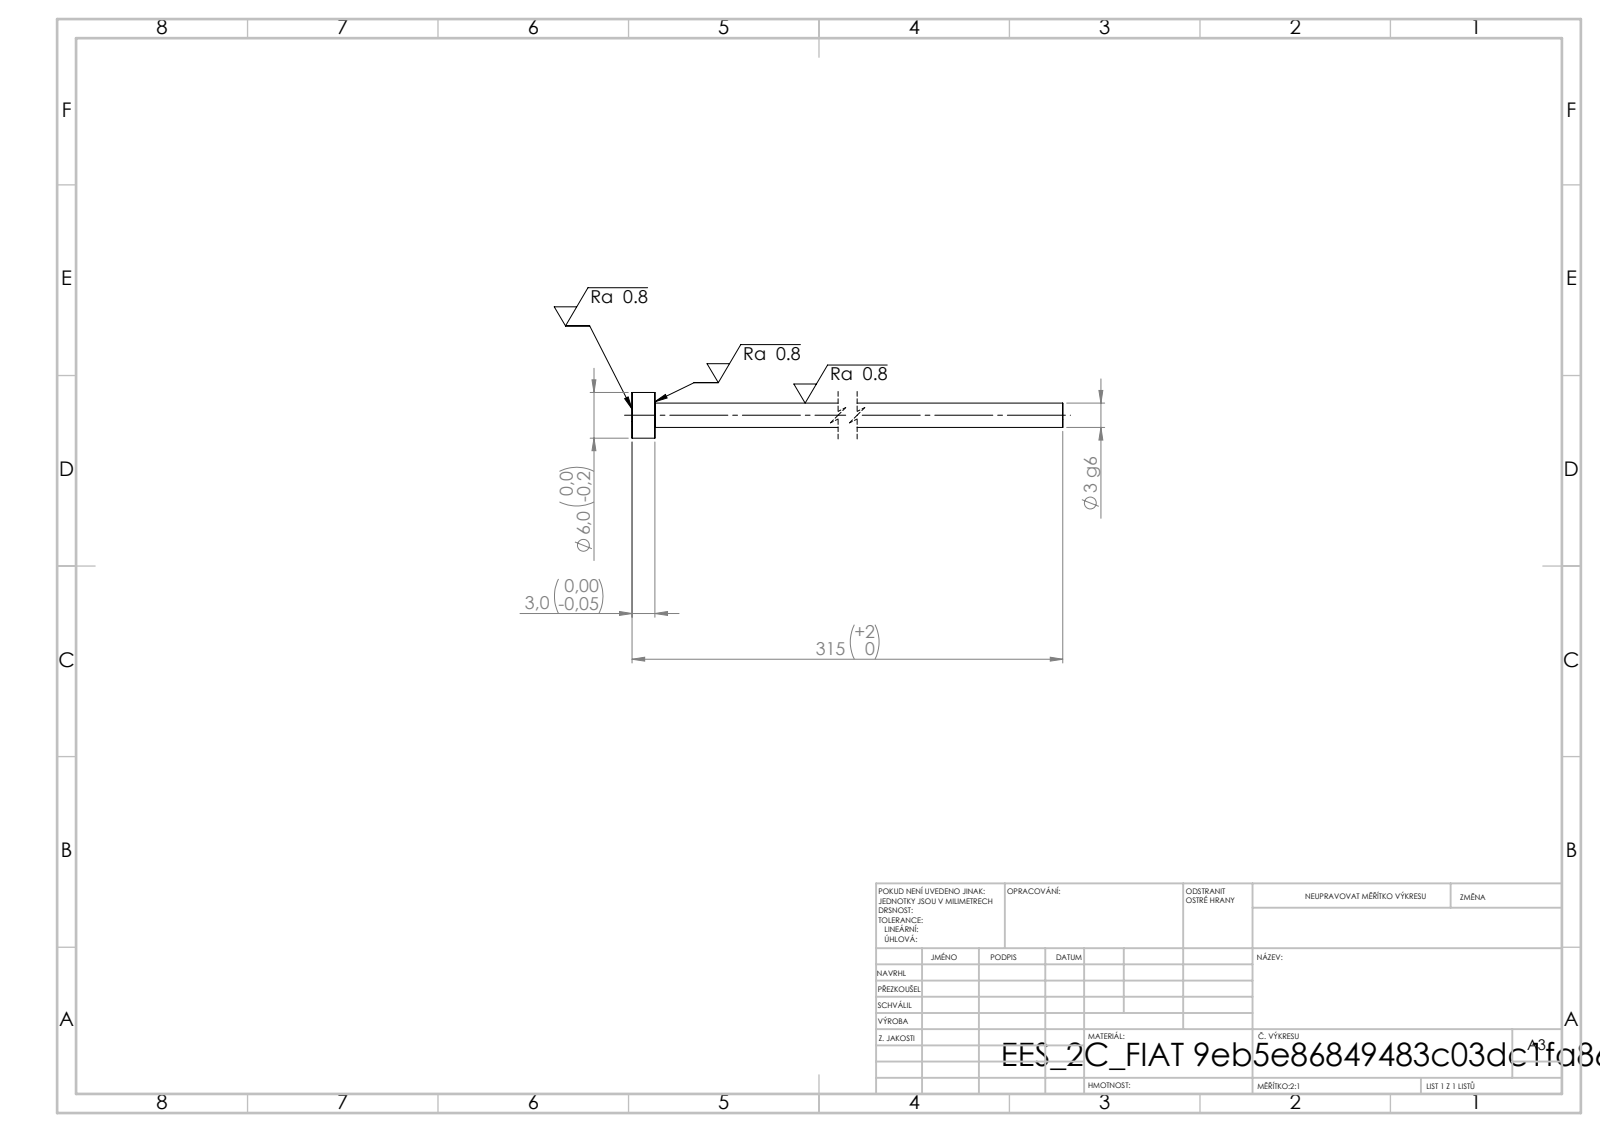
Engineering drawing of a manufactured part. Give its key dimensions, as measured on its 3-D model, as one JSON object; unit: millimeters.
{"step_written_by": "SolidWorks 2019 (CONFIG_CONTROL_DESIGN)", "units": "millimeters", "bodies": {"solids": 1, "faces": 7, "planar": 3, "cylindrical": 4, "other": 0}, "overall_size": [315, 6, 6], "volume_mm3": 2594, "surface_area_mm2": 3250, "round_bosses_or_shafts": [[6, 1], [3.2, 1]], "face_to_face_distances": [3, 315, 312]}
